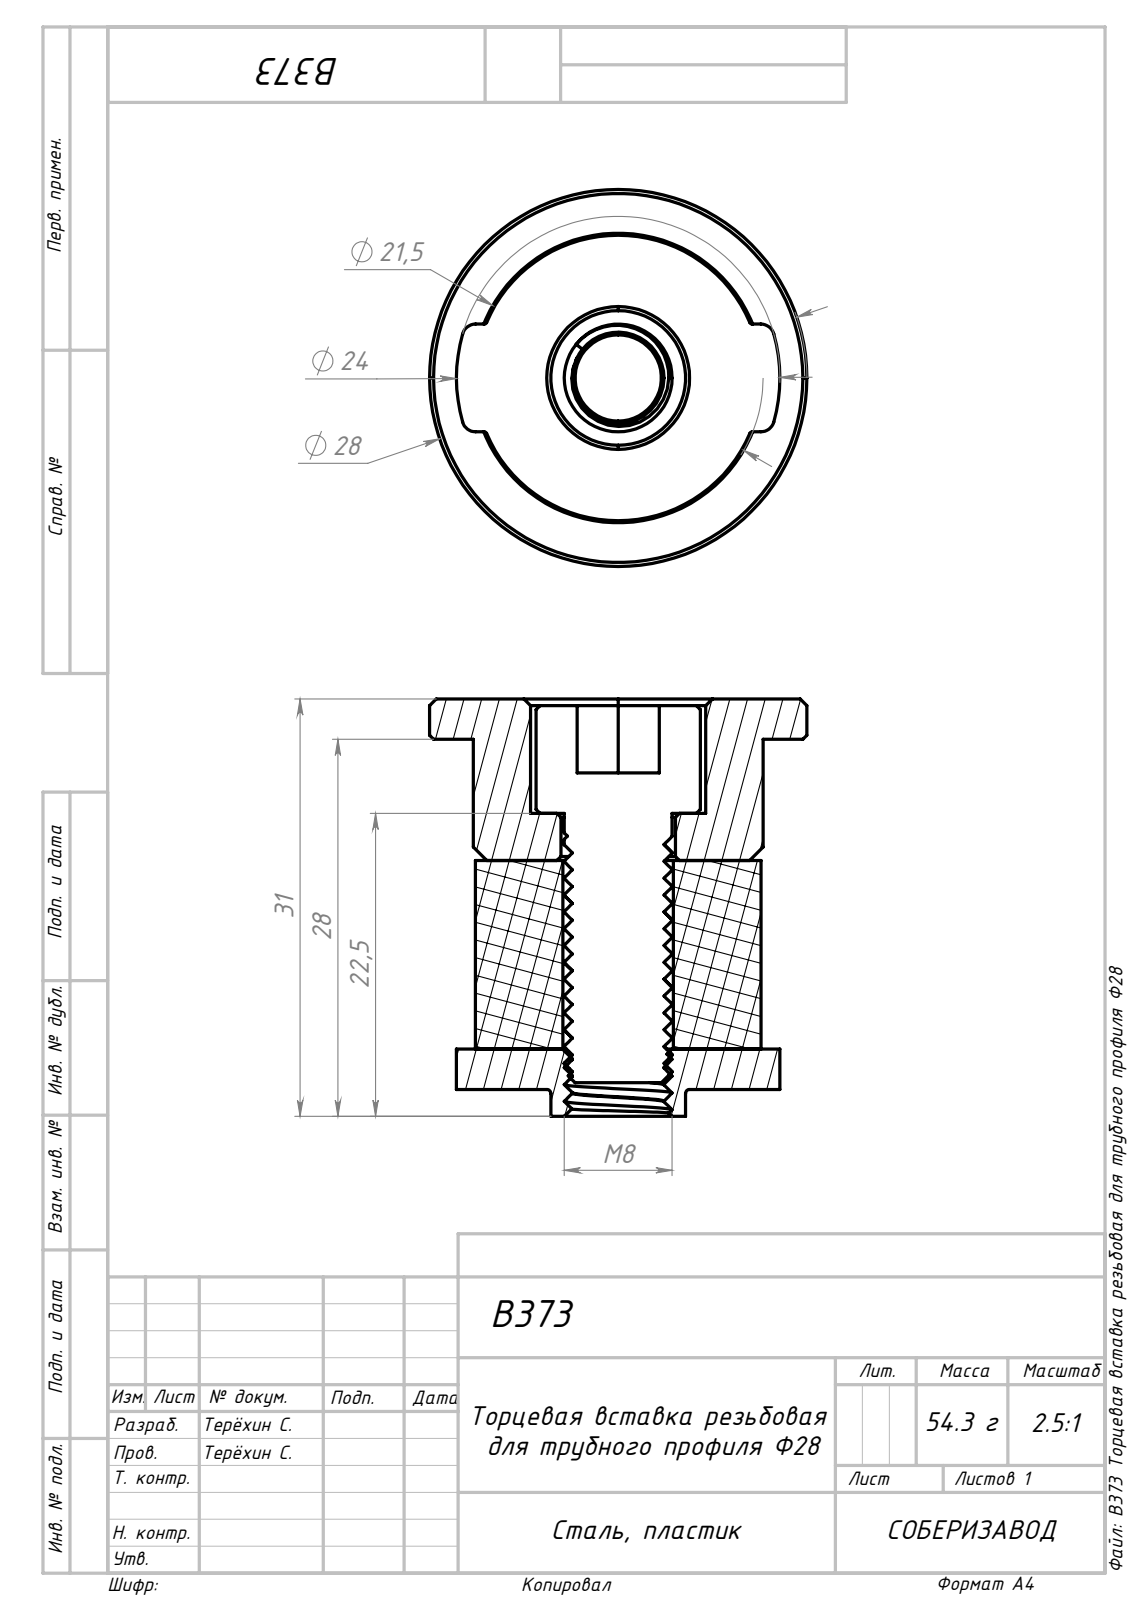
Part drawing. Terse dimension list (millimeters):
name: Сборка1; B373 Торцевая вставка резьбовая для трубного профиля Ф28_00
written by: SolidWorks 2024 (AUTOMOTIVE_DESIGN)
unit: mm
bodies: 4 solids, 131 faces (23 planar, 65 cylindrical, 43 other)
size: 31 × 28 × 28
volume: 10 650 mm³; area: 6 561 mm²
holes: 1× ⌀6.8, 1× ⌀8.2, 1× ⌀8.5, 1× ⌀13
bosses: 1× ⌀28, 1× ⌀21.5, 1× ⌀21.2, 1× ⌀12.2, 1× ⌀10, 1× ⌀8
rounds: 4× R0.2, 4× R1, 1× R12
face distances: 26, 3, 14, 12, 17, 29, 23, 9, 2.5, 20.5
